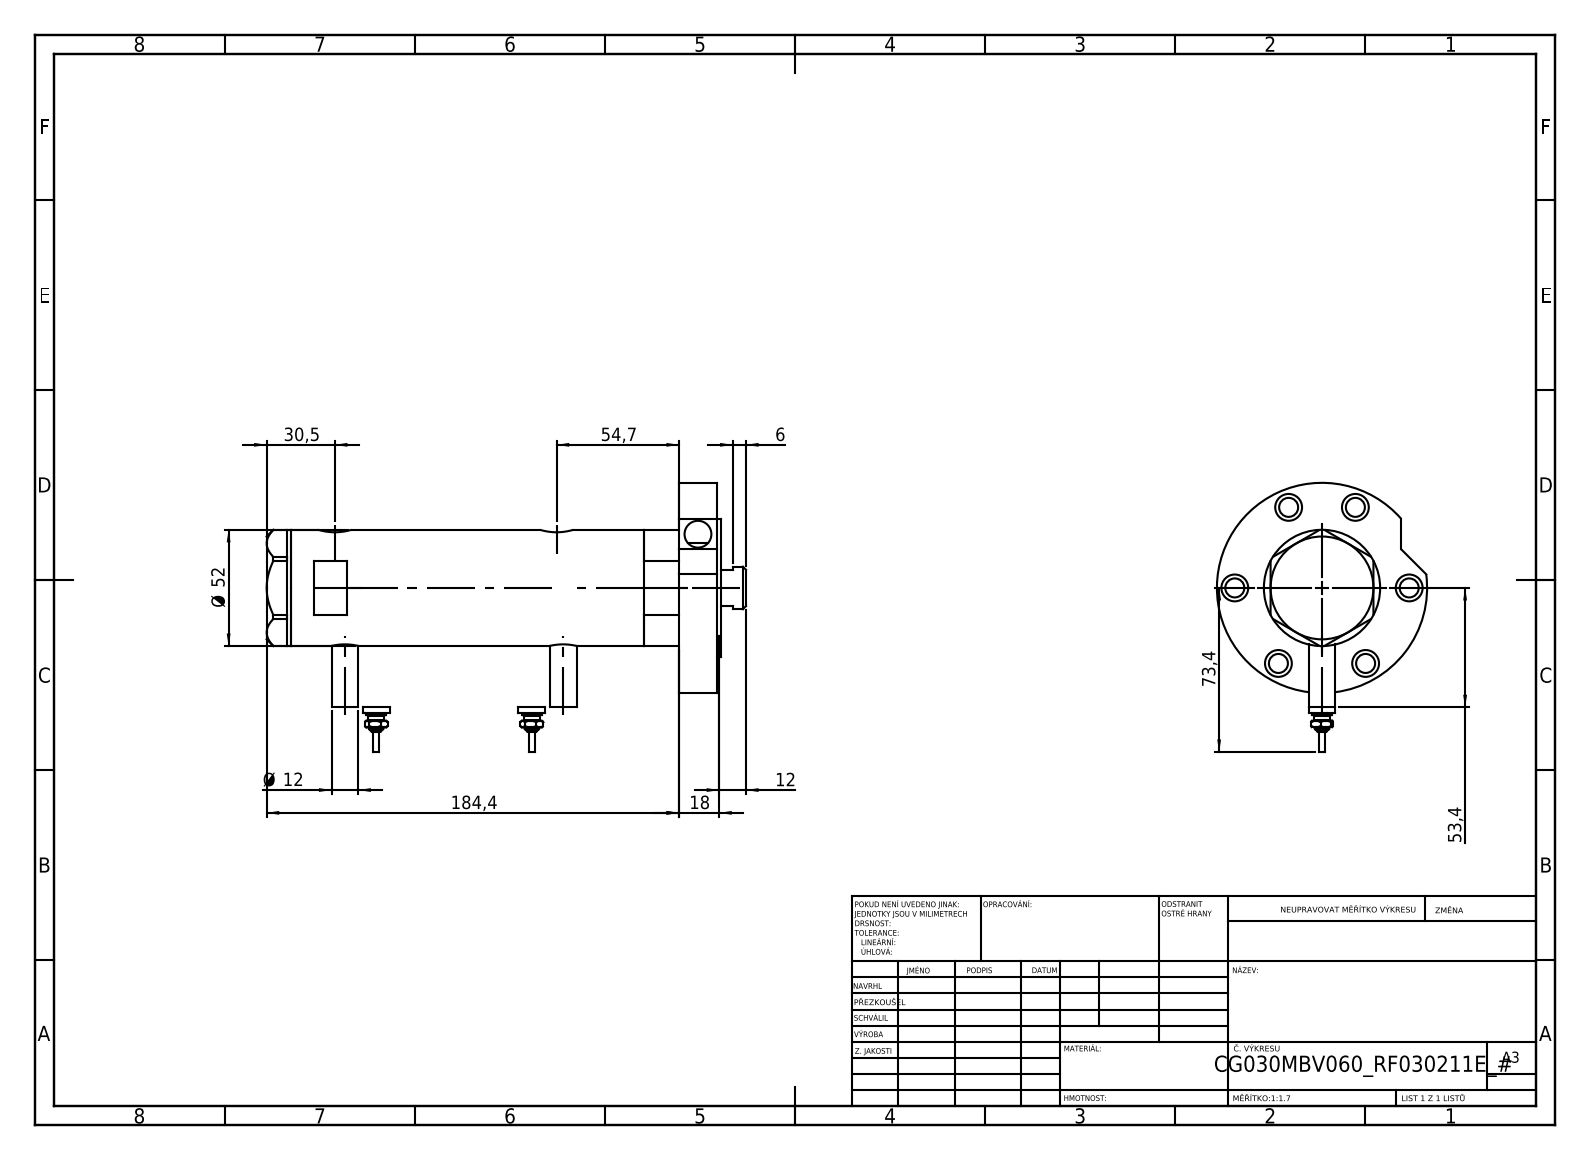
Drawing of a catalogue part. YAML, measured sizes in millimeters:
part_name: "Switch; V270CG_BACK; V270CG_MIDDLE; V270CG_VC (+2 more)"
step_written_by: "SolidWorks 2019 (CONFIG_CONTROL_DESIGN)"
units: millimeters
bodies: {solids: 7, faces: 270, planar: 104, cylindrical: 102, other: 64}
overall_size: [214.4, 120.4, 94]
volume: 474676
surface_area: 113308
round_holes:
  - {diameter: 12, count: 7}
  - {diameter: 8.5, count: 6}
  - {diameter: 9.73, count: 2}
  - {diameter: 12.5, count: 2}
  - {diameter: 15, count: 2}
  - {diameter: 6.5, count: 1}
  - {diameter: 20, count: 1}
  - {diameter: 21.5, count: 1}
  - {diameter: 30, count: 1}
  - {diameter: 33, count: 1}
  - {diameter: 40, count: 1}
  - {diameter: 44, count: 1}
round_bosses_or_shafts:
  - {diameter: 12, count: 4}
  - {diameter: 9, count: 2}
  - {diameter: 7, count: 2}
  - {diameter: 4.5, count: 2}
  - {diameter: 2.5, count: 2}
  - {diameter: 94, count: 1}
  - {diameter: 62, count: 1}
  - {diameter: 52, count: 1}
face_to_face_distances: [17, 173.4, 190.4, 2, 192.4, 121.5, 51.9, 68.9, 11, 203.4]
hole_center_spacings: [39, 43.34, 64.85, 67.55, 69.95, 77.83, 2.9, 4.5]
